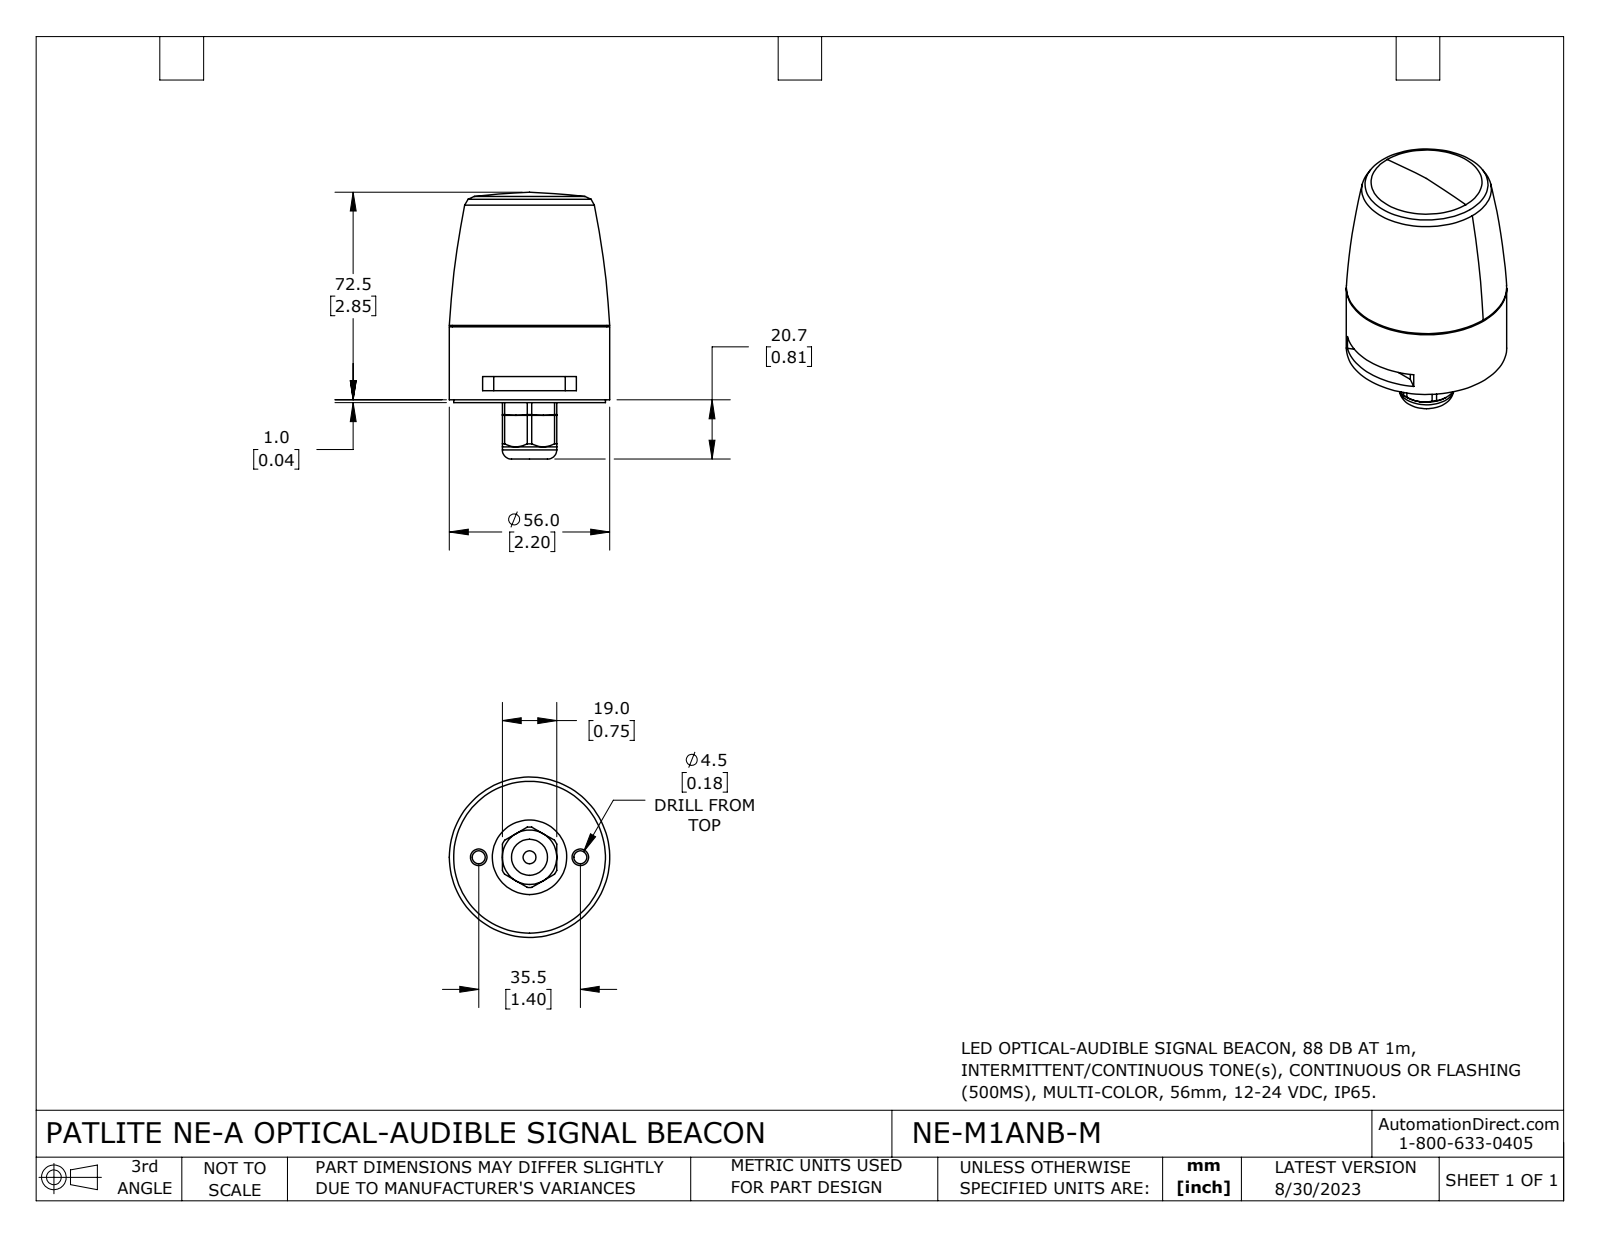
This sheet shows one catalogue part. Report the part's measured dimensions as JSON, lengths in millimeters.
{"part_name": "NE-M1ANB-M", "step_written_by": "SolidWorks 2021 (CONFIG_CONTROL_DESIGN)", "units": "millimeters", "bodies": {"solids": 1, "faces": 133, "planar": 52, "cylindrical": 54, "other": 27}, "overall_size": [93.2, 56, 56], "volume_mm3": 162800, "surface_area_mm2": 18900, "round_holes": [[1.2, 5], [4.5, 3], [5.8, 2], [13.3, 1], [26, 1]], "round_bosses_or_shafts": [[56, 1], [54, 1], [53, 1], [19, 1], [3.6, 1]], "partial_cylinders_radius": [[10.5, 1]], "face_to_face_distances": [1, 19, 4.1, 9.1, 3.1, 8.2, 5, 27, 26, 22.9], "hole_center_spacings": [2.1, 1.3, 1.3, 17.8, 2.1, 35.5]}
